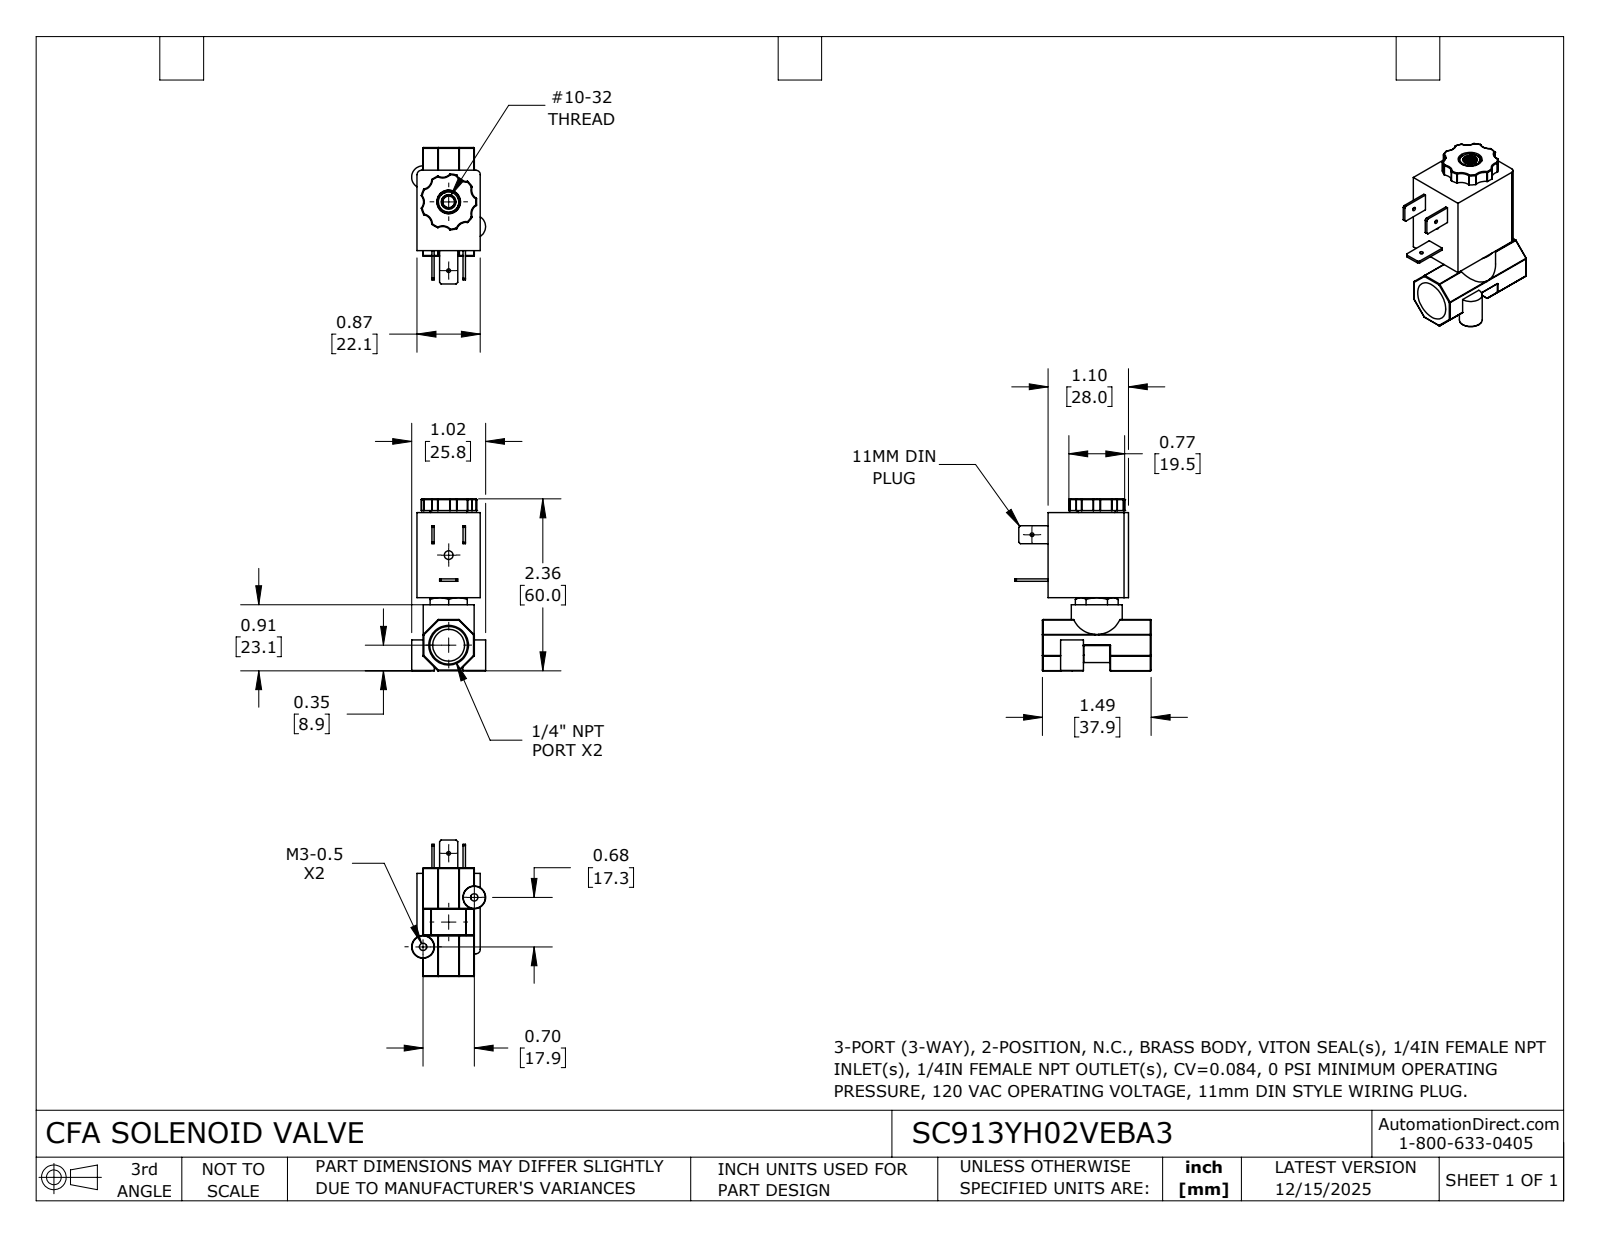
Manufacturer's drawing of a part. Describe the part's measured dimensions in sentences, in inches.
The part is named "SC913YH02VEBA3". Its 3-D file was written by "SolidWorks 2024 (CONFIG_CONTROL_DESIGN)". It is 1 solid with 308 faces: 68 planar, 139 cylindrical and 101 other. Overall it measures 2.363 by 1.874 by 1.017 inches. Its volume is 1.665 cubic inches and its surface area 16.1 square inches. Round holes: 2 of diameter 0.05, 2 of diameter 0.1, 1 of diameter 0.12, 1 of diameter 0.16, 1 of diameter 0.327, 1 of diameter 0.438. Round bosses or shafts: 2 of diameter 0.313, 1 of diameter 0.7, 1 of diameter 0.315. Partial cylindrical surfaces (rounded edges, fillets, slot ends): 42 of radius 0.01, 14 of radius 0.005, 7 of radius 0.133, 2 of radius 0.06, 2 of radius 0.132, 1 of radius 0.237, 1 of radius 0.306, 1 of radius 0.385. The main face-to-face distances are 0.87, 0.704, 1.104, 1.167, 0.083, 0.787, 1.006, 2.173, 2.363, 1.357. The hole center spacings are 0.489, 0.7, 0.945, 0.979, 1.238, 1.333.
